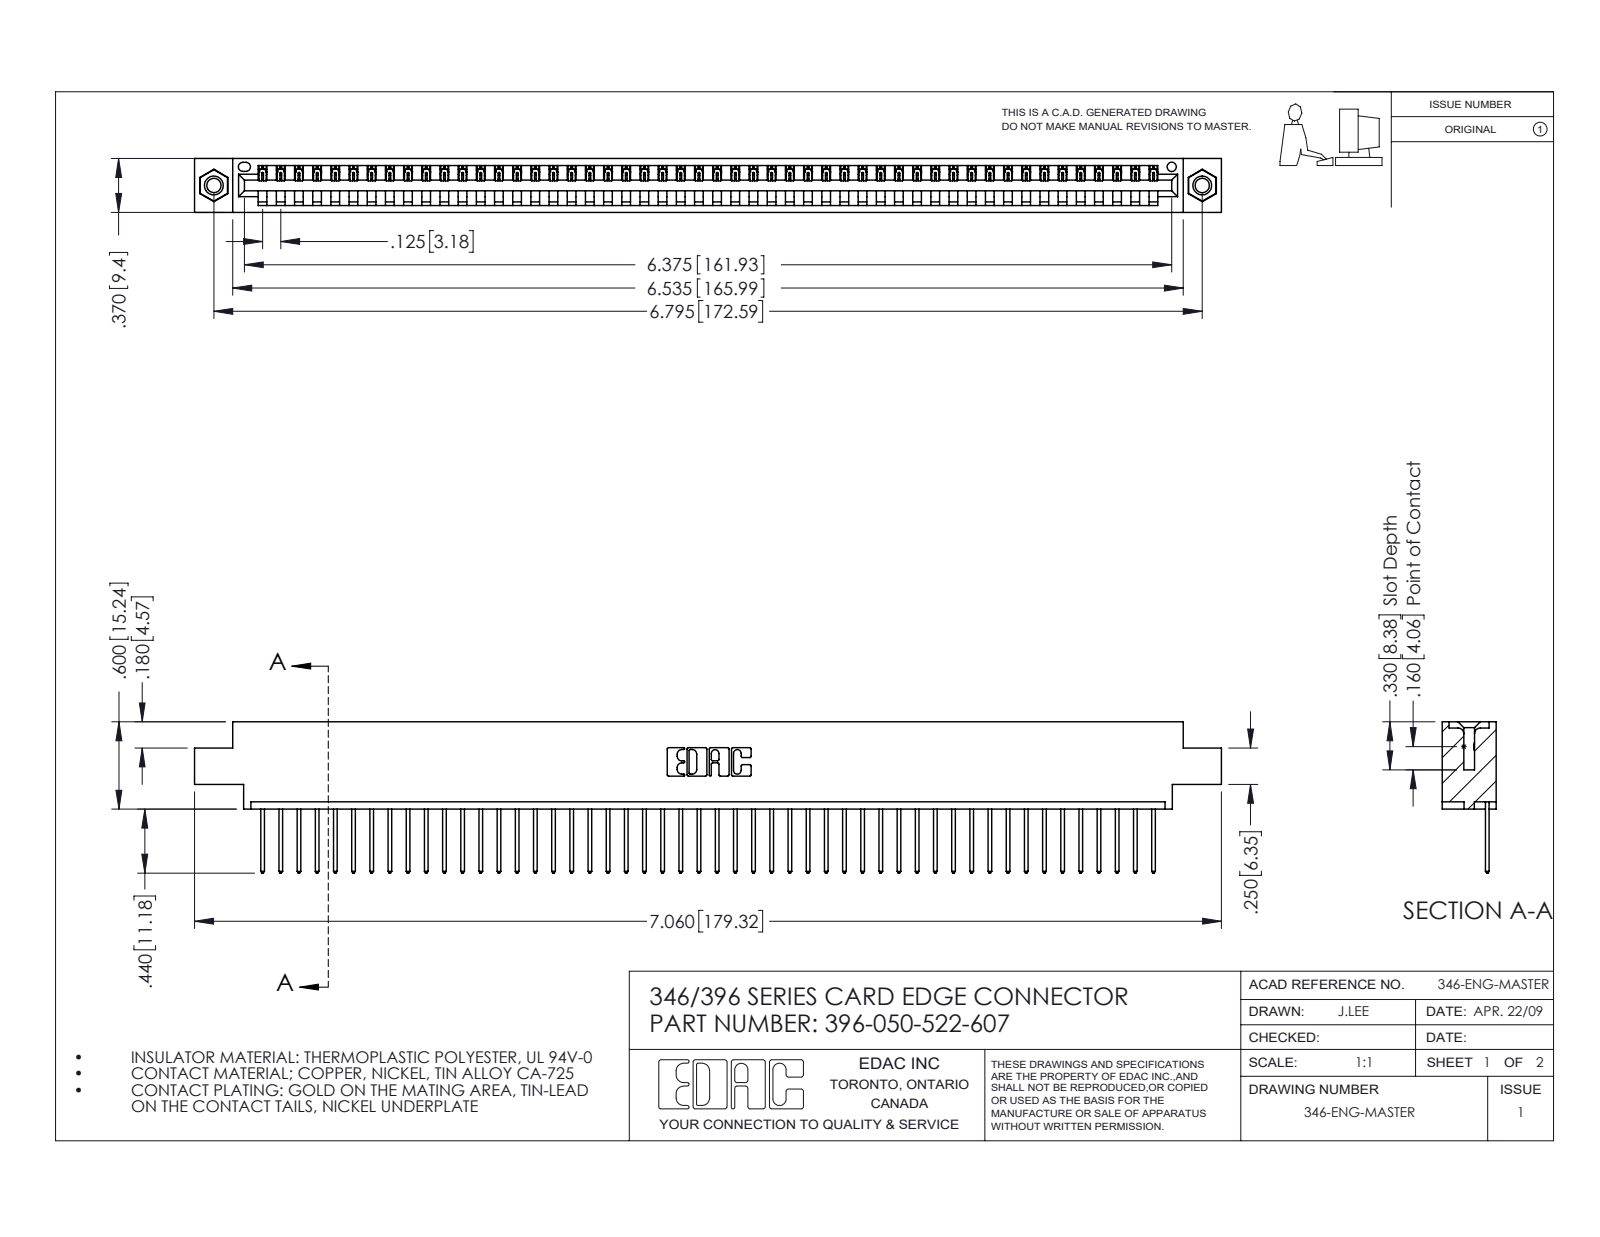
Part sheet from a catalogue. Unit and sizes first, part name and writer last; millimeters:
Units: millimetres
Overall size (bounding box): 179.3 × 26.4 × 9.4
Round holes (diameter × count): ⌀2.5 ×2, ⌀3.2 ×2, ⌀4 ×2, ⌀1.6 ×1
Round bosses / shafts (diameter × count): ⌀3.9 ×2
Partial cylindrical surfaces — rounded edges, fillets, slot ends (radius × count): R0.2 ×100, R0.3 ×100, R0.3 ×22, R0.2 ×6, R0.8 ×6, R0.7 ×3, R0.8 ×2, R1 ×2
Main face-to-face distances: 1.2, 8.2, 9.4, 6.4, 1.8, 7.6, 0.6, 5.6, 3.8, 2.5
Hole centre spacings: 6.2, 167.3, 172.6
Volume: 17 060 mm³ · Surface area: 21 790 mm²
Bodies: 53 solids, 3086 faces (2112 planar, 958 cylindrical, 16 other)
Part name (STEP PRODUCT): 396-050-522-607; 345-292-001_345-293-122; 345-250-001_345-250-005-103; 346 Part_0.170 Offset - 0.156 Dia-TI
STEP written by: SolidWorks 2016 (CONFIG_CONTROL_DESIGN)
